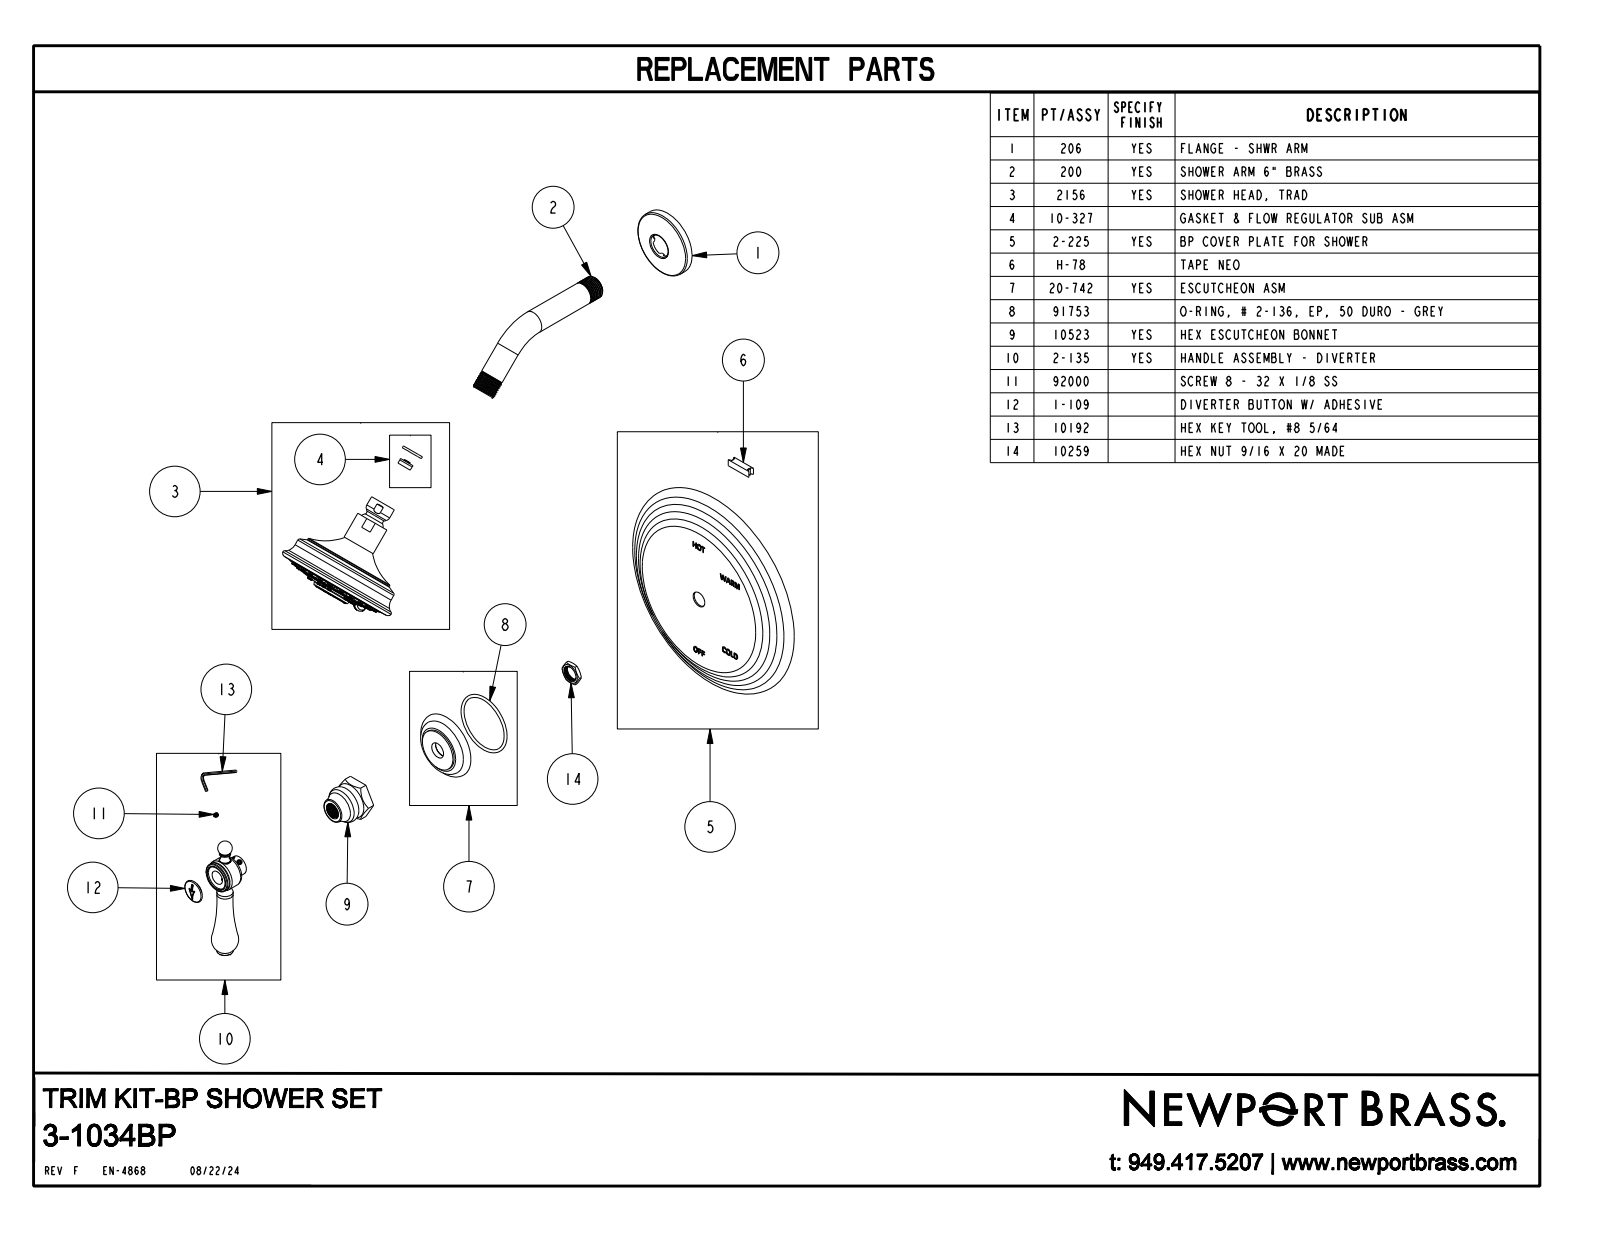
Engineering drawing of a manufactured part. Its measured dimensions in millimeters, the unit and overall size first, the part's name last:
Units: millimetres
Overall size (bounding box): 484.3 × 209.6 × 196.9
Round holes (diameter × count): ⌀1.5 ×8, ⌀10.4 ×1, ⌀21.7 ×1, ⌀23.5 ×1
Round bosses / shafts (diameter × count): ⌀3.6 ×39, ⌀4.2 ×23, ⌀20.7 ×2, ⌀96.8 ×1, ⌀94.6 ×1, ⌀82.3 ×1, ⌀60.5 ×1, ⌀59 ×1
Partial cylindrical surfaces — rounded edges, fillets, slot ends (radius × count): R2 ×8, R0.4 ×2, R0.5 ×2, R25.4 ×2, R25.9 ×2, R0.5 ×1, R3.5 ×1, R12 ×1
Main face-to-face distances: 19.2, 1.6, 3, 4.6, 33.4, 1.6, 62, 42.8, 28.7, 9.5
Hole centre spacings: 11.3, 27.2, 20.8, 14.7, 14.7, 20.8, 29.4, 29.4
Volume: 858 200 mm³ · Surface area: 125 700 mm²
Bodies: 2 solids, 1396 faces (296 planar, 223 cylindrical, 877 other)
Part name (STEP PRODUCT): 3-1034BP
STEP written by: CREO PARAMETRIC BY PTC INC, 2018400 (CONFIG_CONTROL_DESIGN)
